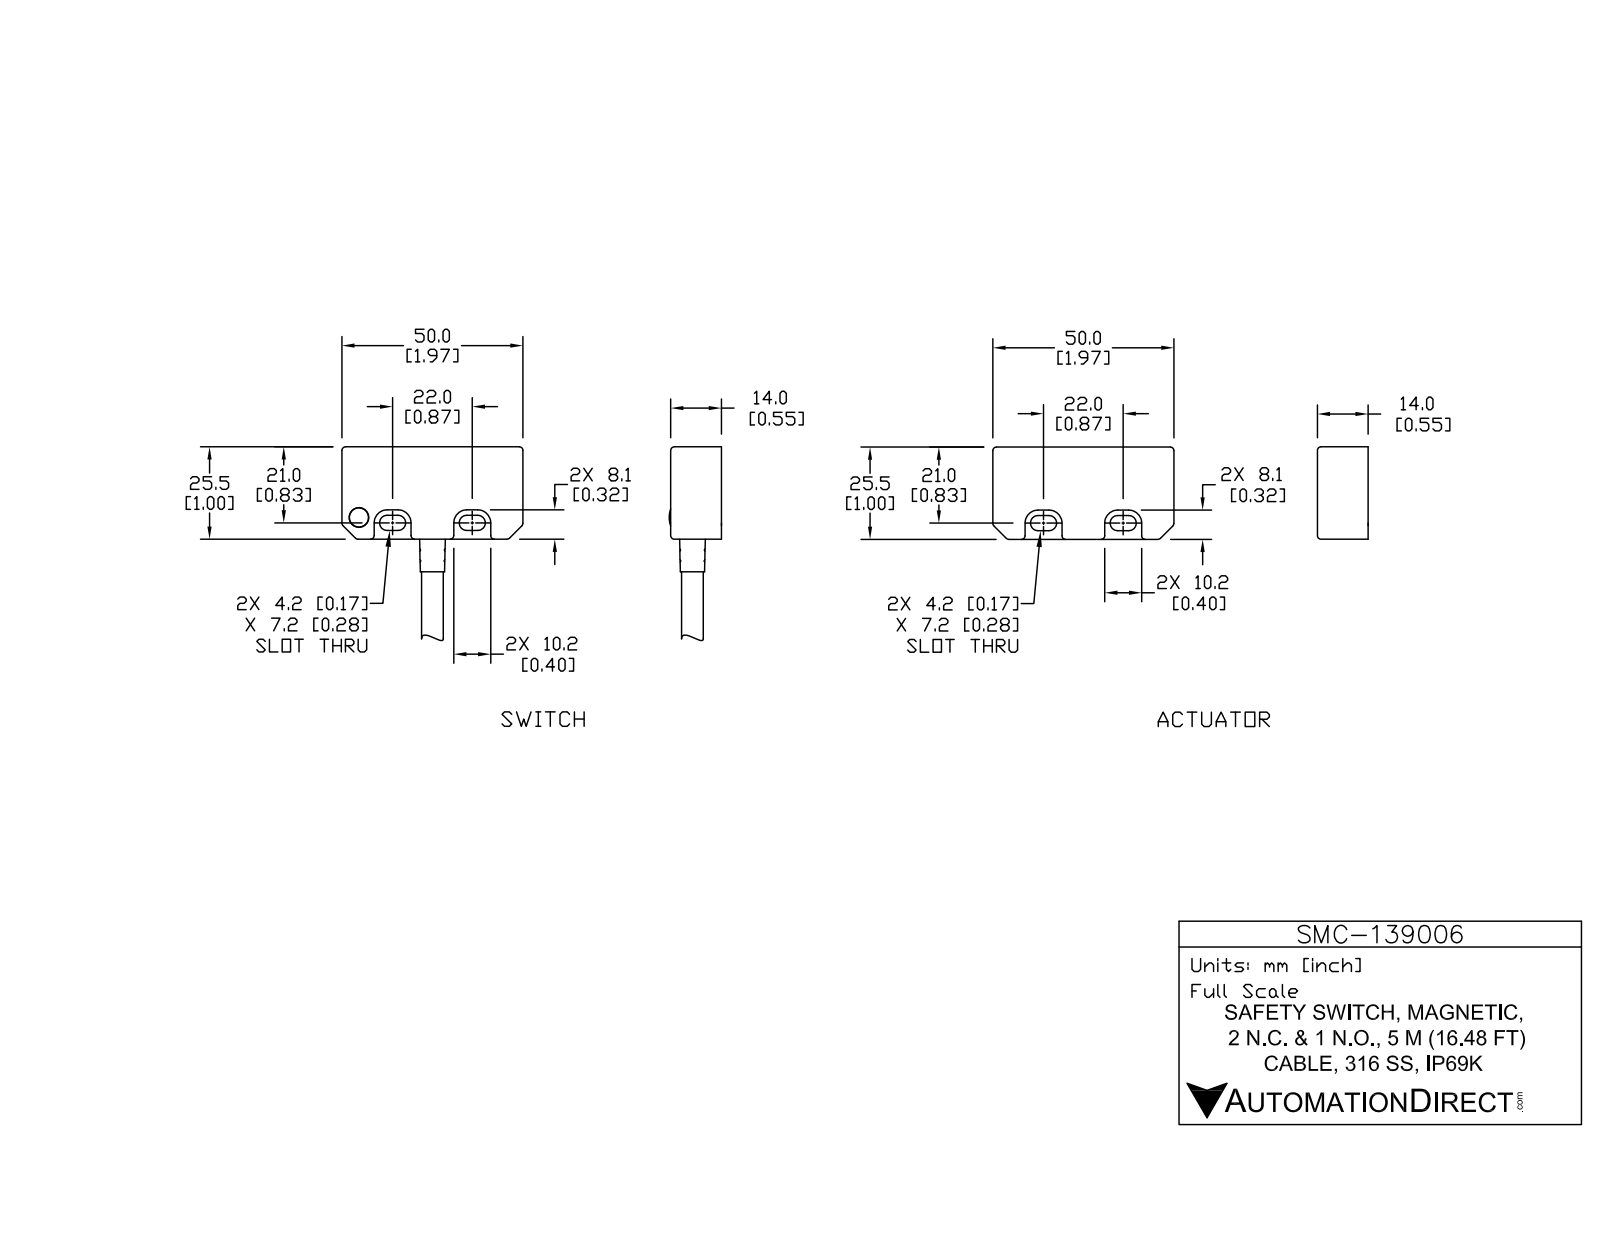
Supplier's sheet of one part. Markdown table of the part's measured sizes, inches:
| quantity | value |
| --- | --- |
| part name | SMC-139006_1; SMC-139006; SMC-139006_2 |
| STEP written by | SolidWorks 2017 (AUTOMOTIVE_DESIGN) |
| units | inches |
| bodies | 12 solids, 886 faces (254 planar, 373 cylindrical, 259 other) |
| overall size | 8.091 × 1.969 × 0.566 |
| volume | 1.16 in³ |
| surface area | 36.28 in² |
| round holes (diameter × count) | 0.197 × 4, 0.119 × 1, 0.177 × 1, 0.213 × 1, 0.232 × 1, 0.287 × 1 |
| round bosses / shafts (diameter × count) | 0.193 × 4, 0.079 × 4, 0.031 × 2, 0.339 × 1, 0.299 × 1, 0.28 × 1, 0.236 × 1, 0.209 × 1 |
| partial cylindrical surfaces (radius × count) | 0.02 × 80, 0.012 × 74, 0.039 × 40, 0.083 × 8, 0.122 × 8, 0.128 × 8, 0.142 × 8, 0.175 × 8 |
| main face-to-face distances | 0.059, 0.543, 0.055, 0.488, 0.484, 0.429, 0.098, 0.945, 1.043, 1.909 |
| hole center spacings | 0.866, 0.988, 0.472, 1.27, 1.309, 1.319, 1.332, 1.775 |
